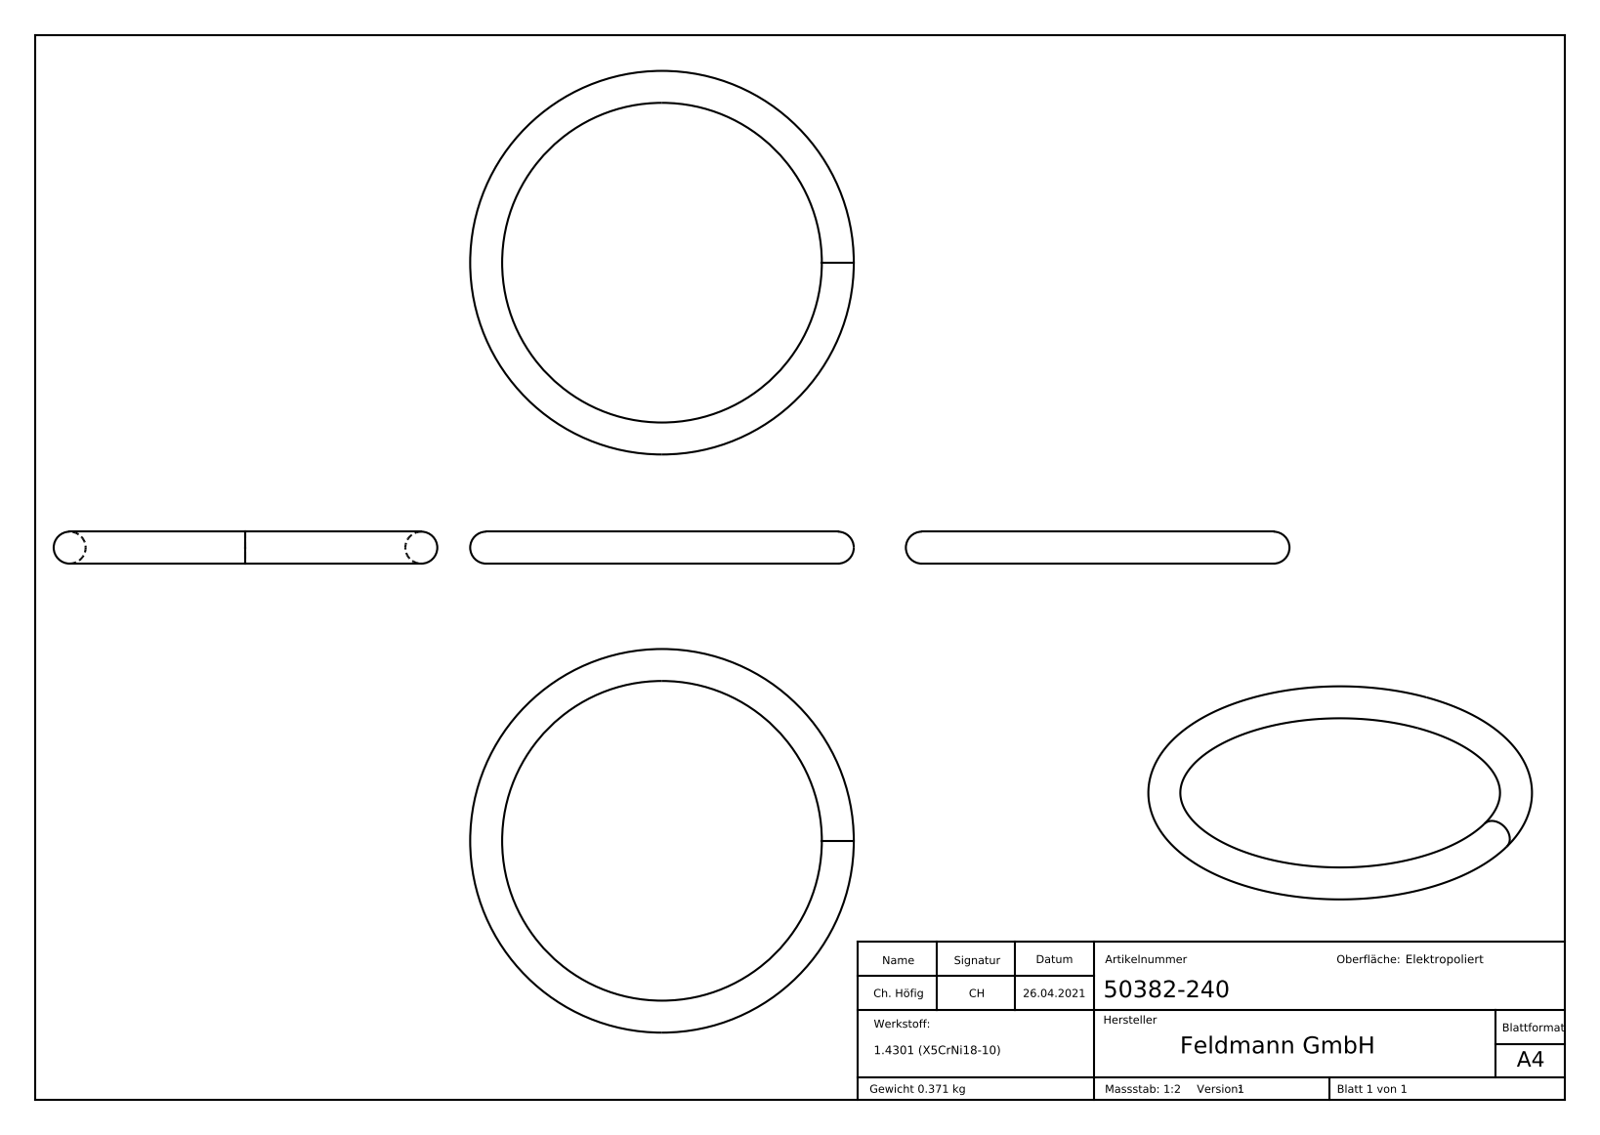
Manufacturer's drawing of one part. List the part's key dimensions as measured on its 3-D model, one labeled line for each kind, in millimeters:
Part name (STEP PRODUCT): 50382-240
STEP written by: SolidWorks 2018 (CONFIG_CONTROL_DESIGN)
Units: millimetres
Bodies: 1 solid, 4 faces (0 planar, 0 cylindrical, 4 other)
Overall size (bounding box): 144 × 144 × 12
Volume: 46 900 mm³ · Surface area: 15 633 mm²
